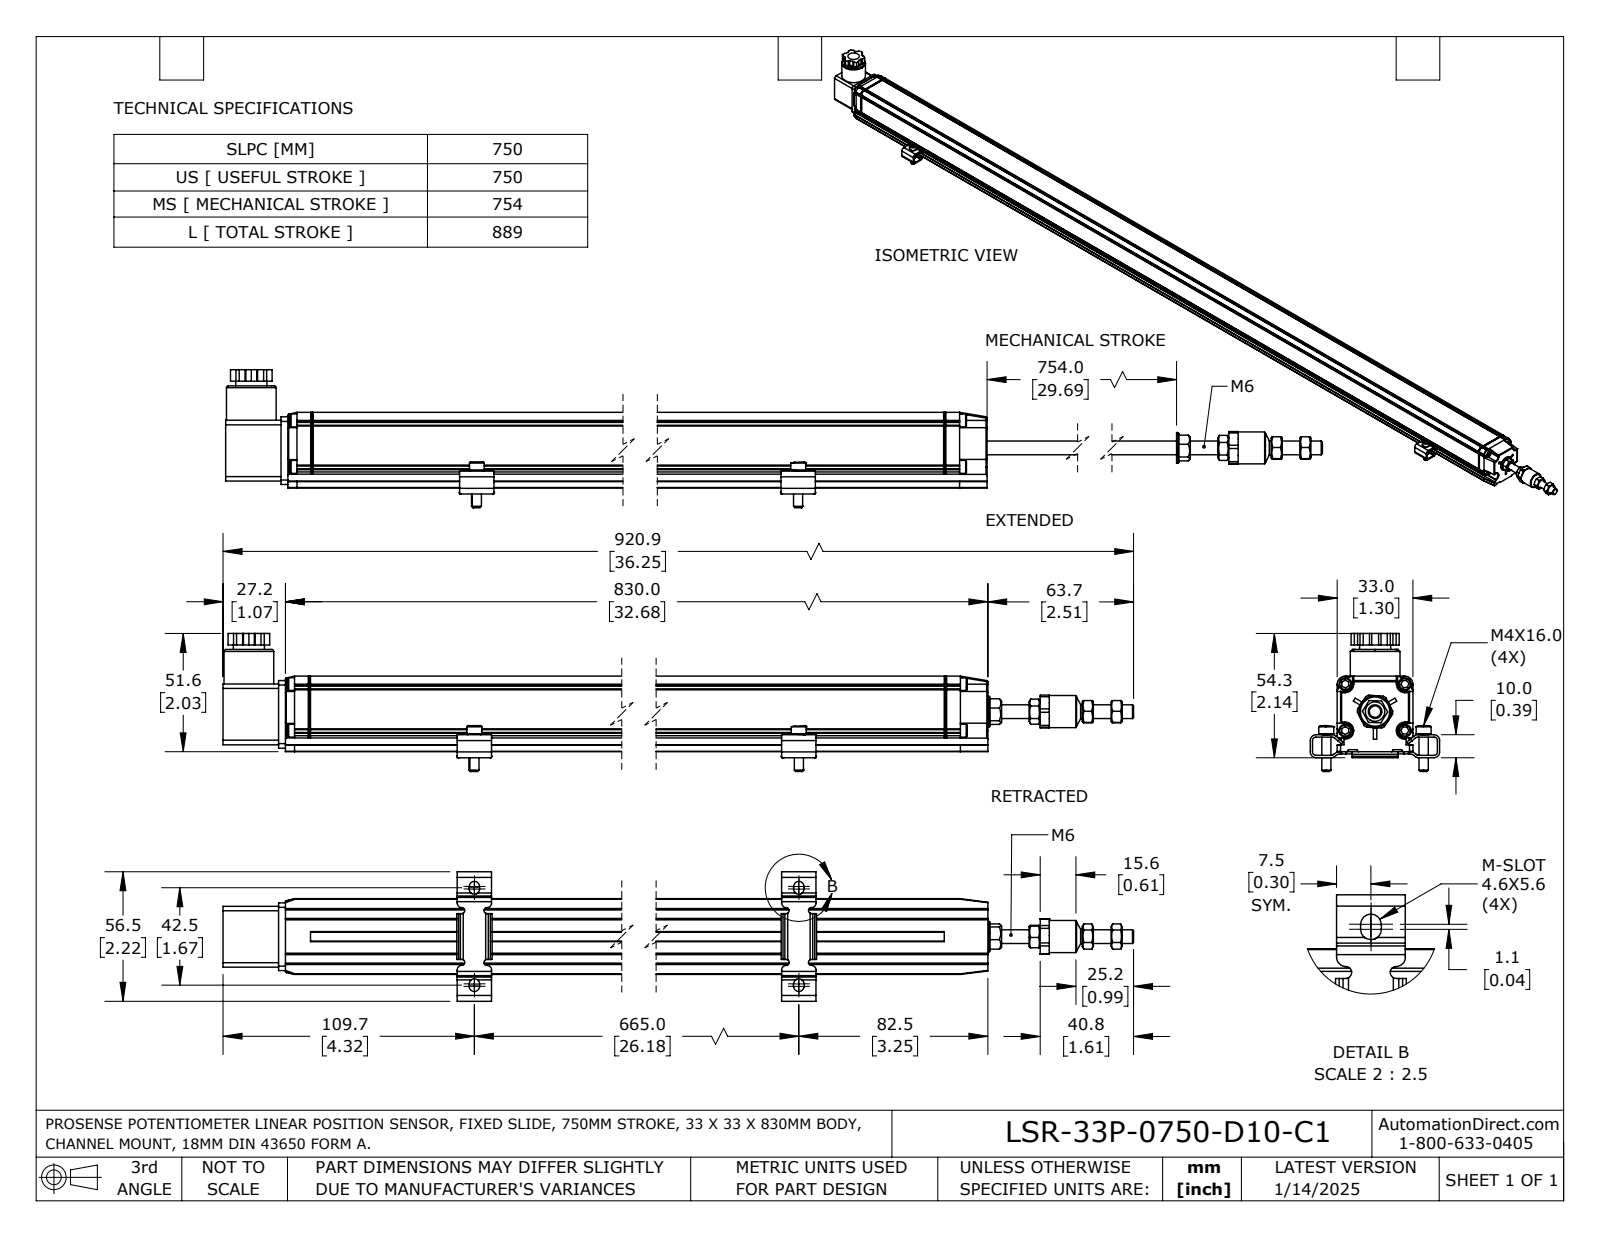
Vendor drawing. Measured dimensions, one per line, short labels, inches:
name: LSR-33P-0750-D10-C1
written by: SolidWorks 2023 (AUTOMOTIVE_DESIGN)
unit: in
bodies: 14 solids, 995 faces (641 planar, 269 cylindrical, 85 other)
size: 36.254 × 2.37 × 2.224
volume: 50.76 in³; area: 304.7 in²
holes: 4× ⌀0.106, 4× ⌀0.13, 1× ⌀0.169, 1× ⌀0.205, 1× ⌀0.209, 1× ⌀0.232, 1× ⌀0.276, 1× ⌀0.285, 1× ⌀0.394, 1× ⌀0.413, 1× ⌀0.573, 1× ⌀0.602
bosses: 5× ⌀0.157, 5× ⌀0.118, 4× ⌀0.256, 4× ⌀0.22, 1× ⌀0.854, 1× ⌀0.551, 1× ⌀0.535, 1× ⌀0.528
rounds: 28× R0.079, 23× R0.02, 16× R0.008, 8× R0.051, 8× R0.059, 8× R0.089, 8× R0.118, 4× R0.039
face distances: 1.299, 0.118, 0.22, 1.181, 1.079, 0.039, 0.079, 0.142, 1.22, 0.185
hole spacings: 0.047, 0.583, 0.607, 0.696, 0.73, 0.799, 1.024, 1.299
